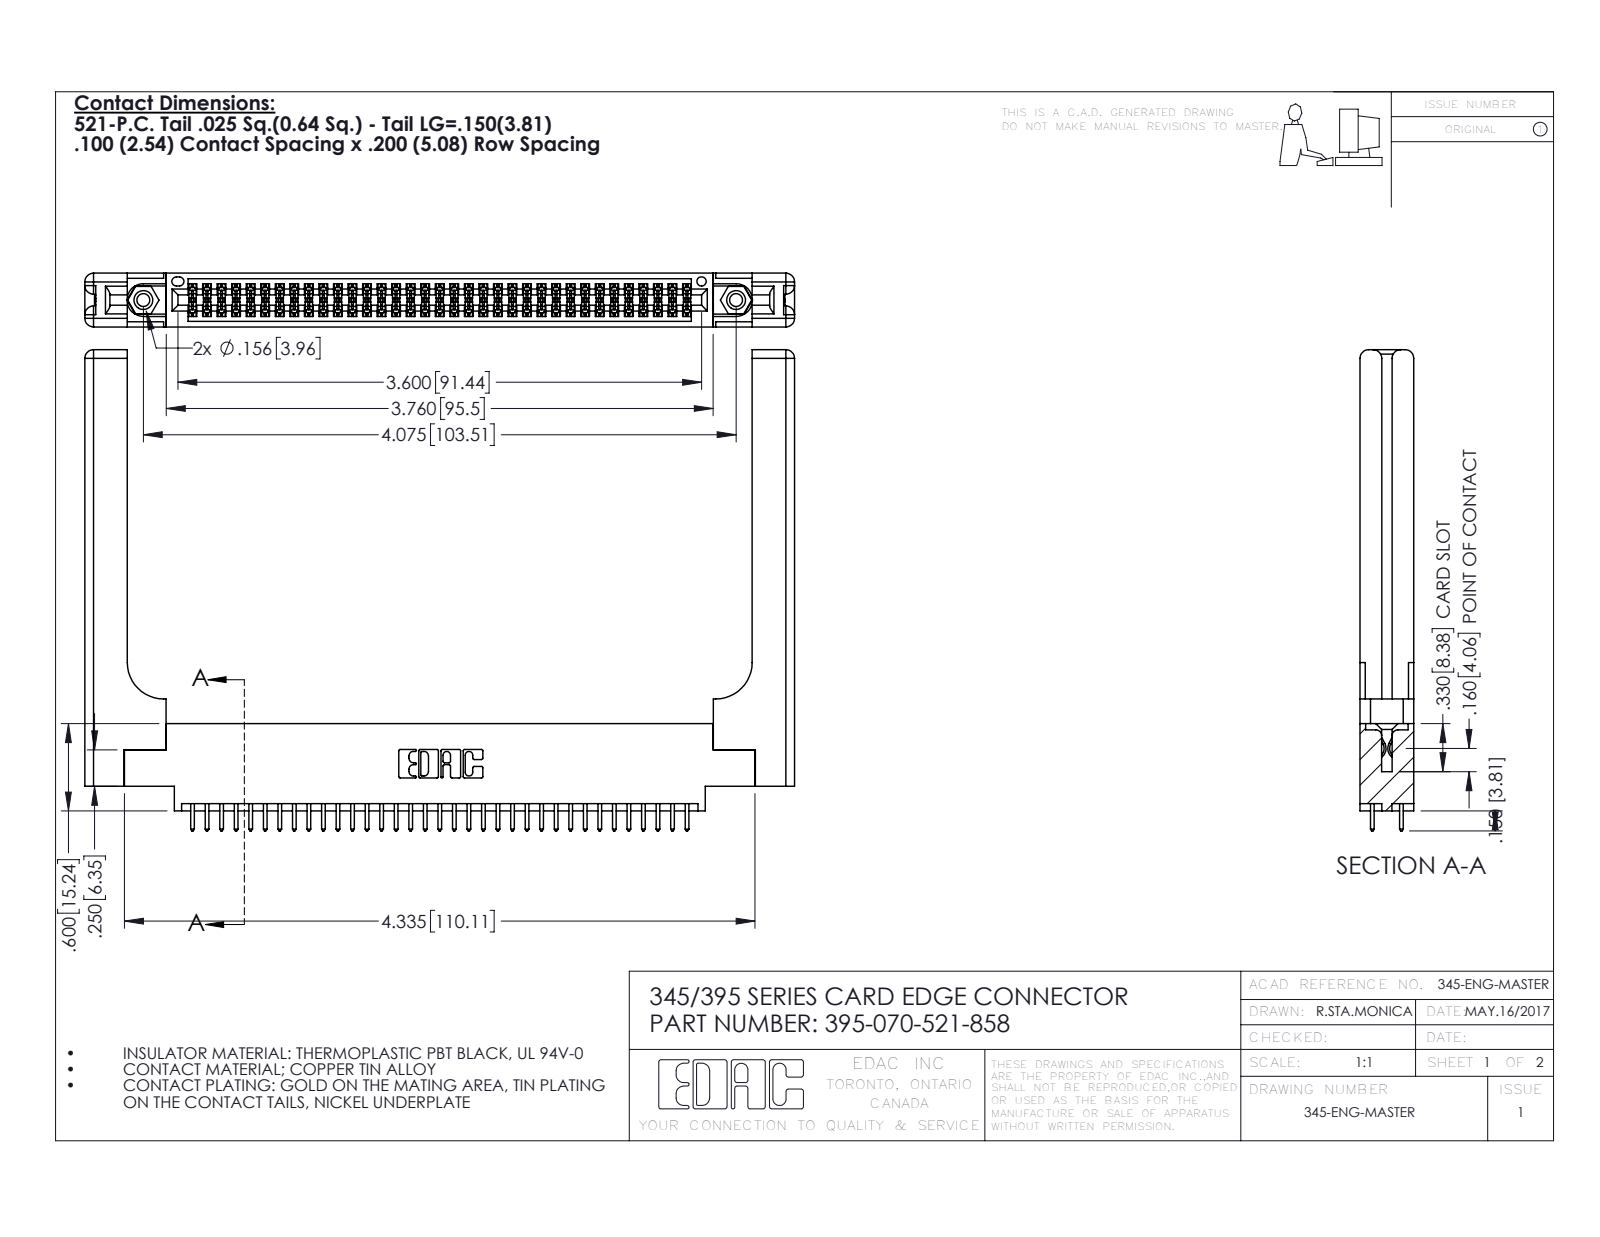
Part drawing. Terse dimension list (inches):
name: 395-070-521-858; 345-292-001_345-293-121; 345-220-058_345-220-058; 345 Part_0.170 Offset - 0.156 Dia-TH (+1 more)
written by: SolidWorks 2016 (CONFIG_CONTROL_DESIGN)
unit: in
bodies: 75 solids, 3886 faces (2542 planar, 1284 cylindrical, 60 other)
size: 4.879 × 3.307 × 0.37
volume: 1.239 in³; area: 34.67 in²
holes: 2× ⌀0.089, 2× ⌀0.125, 2× ⌀0.156, 1× ⌀0.064
bosses: 2× ⌀0.155
rounds: 105× R0.006, 70× R0.01, 22× R0.01, 16× R0.06, 6× R0.007, 6× R0.031, 3× R0.026, 2× R0.014
face distances: 0.37, 0.072, 0.298, 0.098, 0.272, 0.025, 0.2, 0.225, 0.148, 0.15
hole spacings: 0.27, 3.839, 4.075
